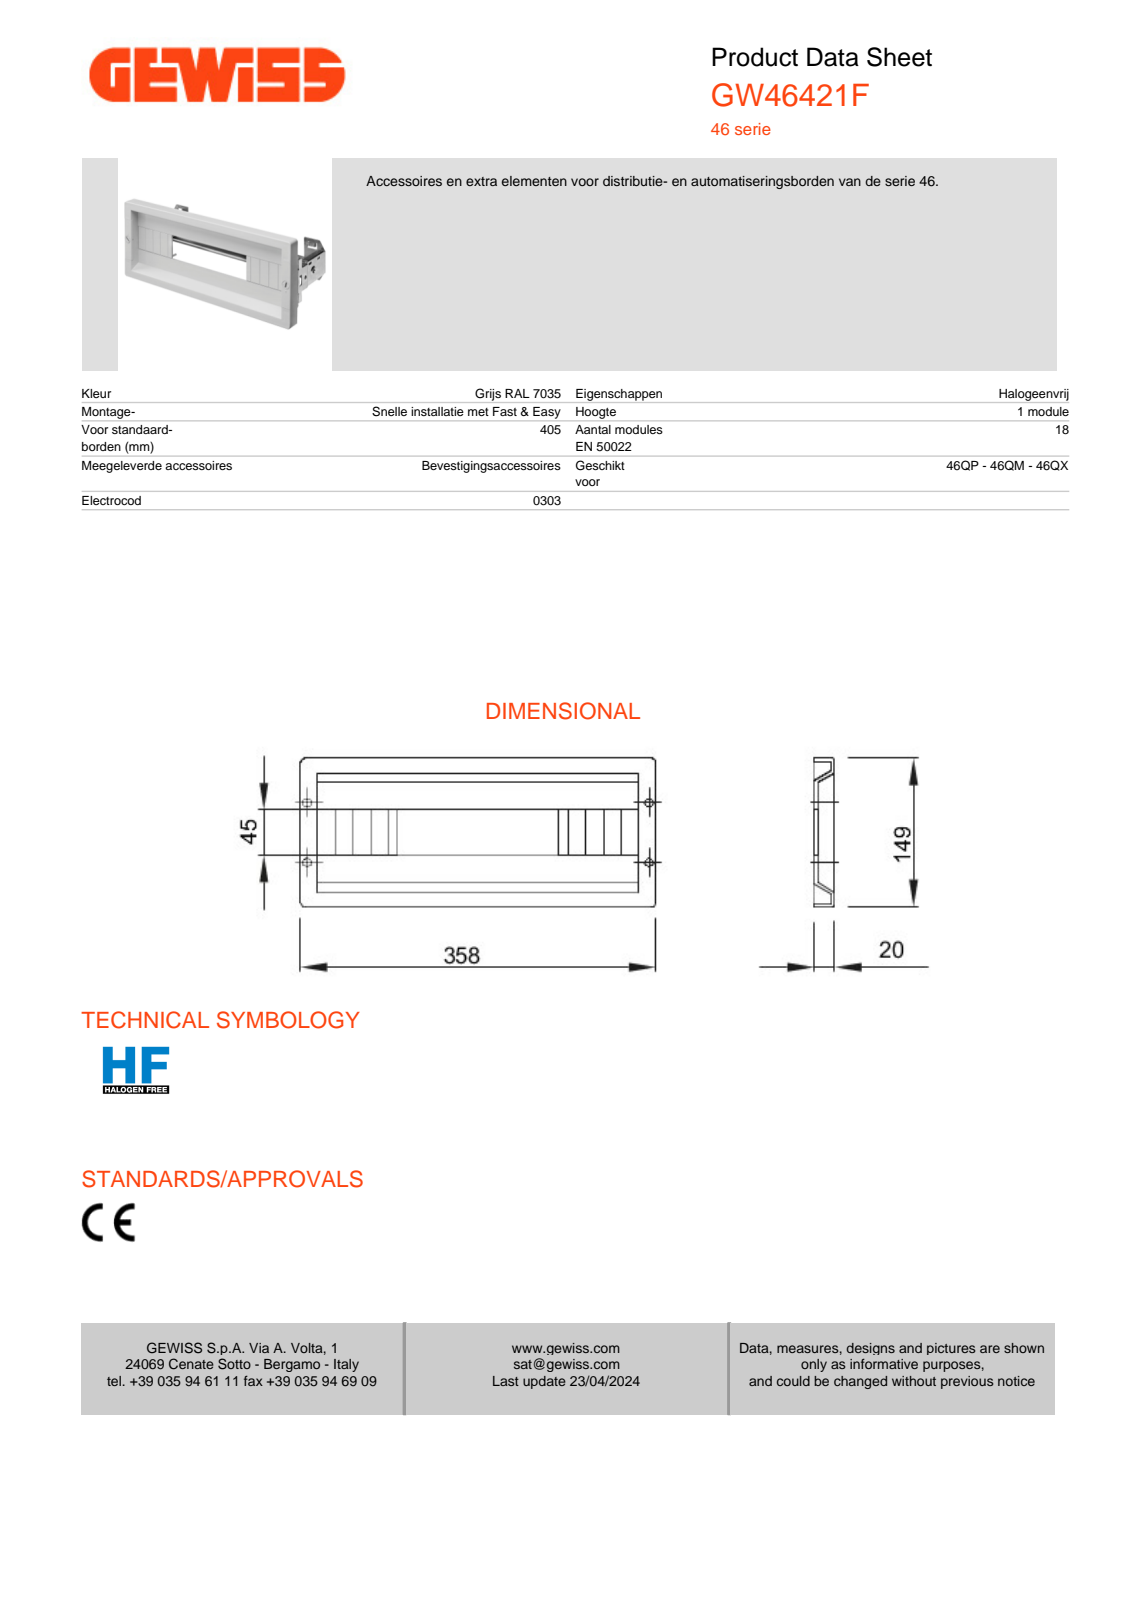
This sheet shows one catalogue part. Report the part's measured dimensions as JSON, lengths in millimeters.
{"part_name": "55721435XXXX_GUIDA_DIN_18M_H15; 55710602_D2_MOSTRINA_CON_FINEST; GW46421F_ASM", "step_written_by": "CREO PARAMETRIC BY PTC INC, 2020354 (CONFIG_CONTROL_DESIGN)", "units": "millimeters", "bodies": {"solids": 2, "faces": 1050, "planar": 742, "cylindrical": 256, "other": 52}, "overall_size": [363, 149, 119.87], "volume_mm3": 287642, "surface_area_mm2": 251805, "round_holes": [[4.5, 4], [6.5, 4], [3.24, 2], [4.2, 2], [4.6, 2], [5.5, 2], [6, 1], [8, 1]], "round_bosses_or_shafts": [[14.4, 2], [13.4, 2], [9.6, 2]], "partial_cylinders_radius": [[1.5, 44], [1, 38], [0.5, 16], [1.15, 8], [1.25, 8], [2, 6], [0.25, 4], [4, 4]], "face_to_face_distances": [3, 1.5, 17, 20, 146, 14, 64, 81, 32.5, 62.5], "hole_center_spacings": [323.5, 14.5, 309, 30.23, 35.11, 328.62, 338, 343.06]}
